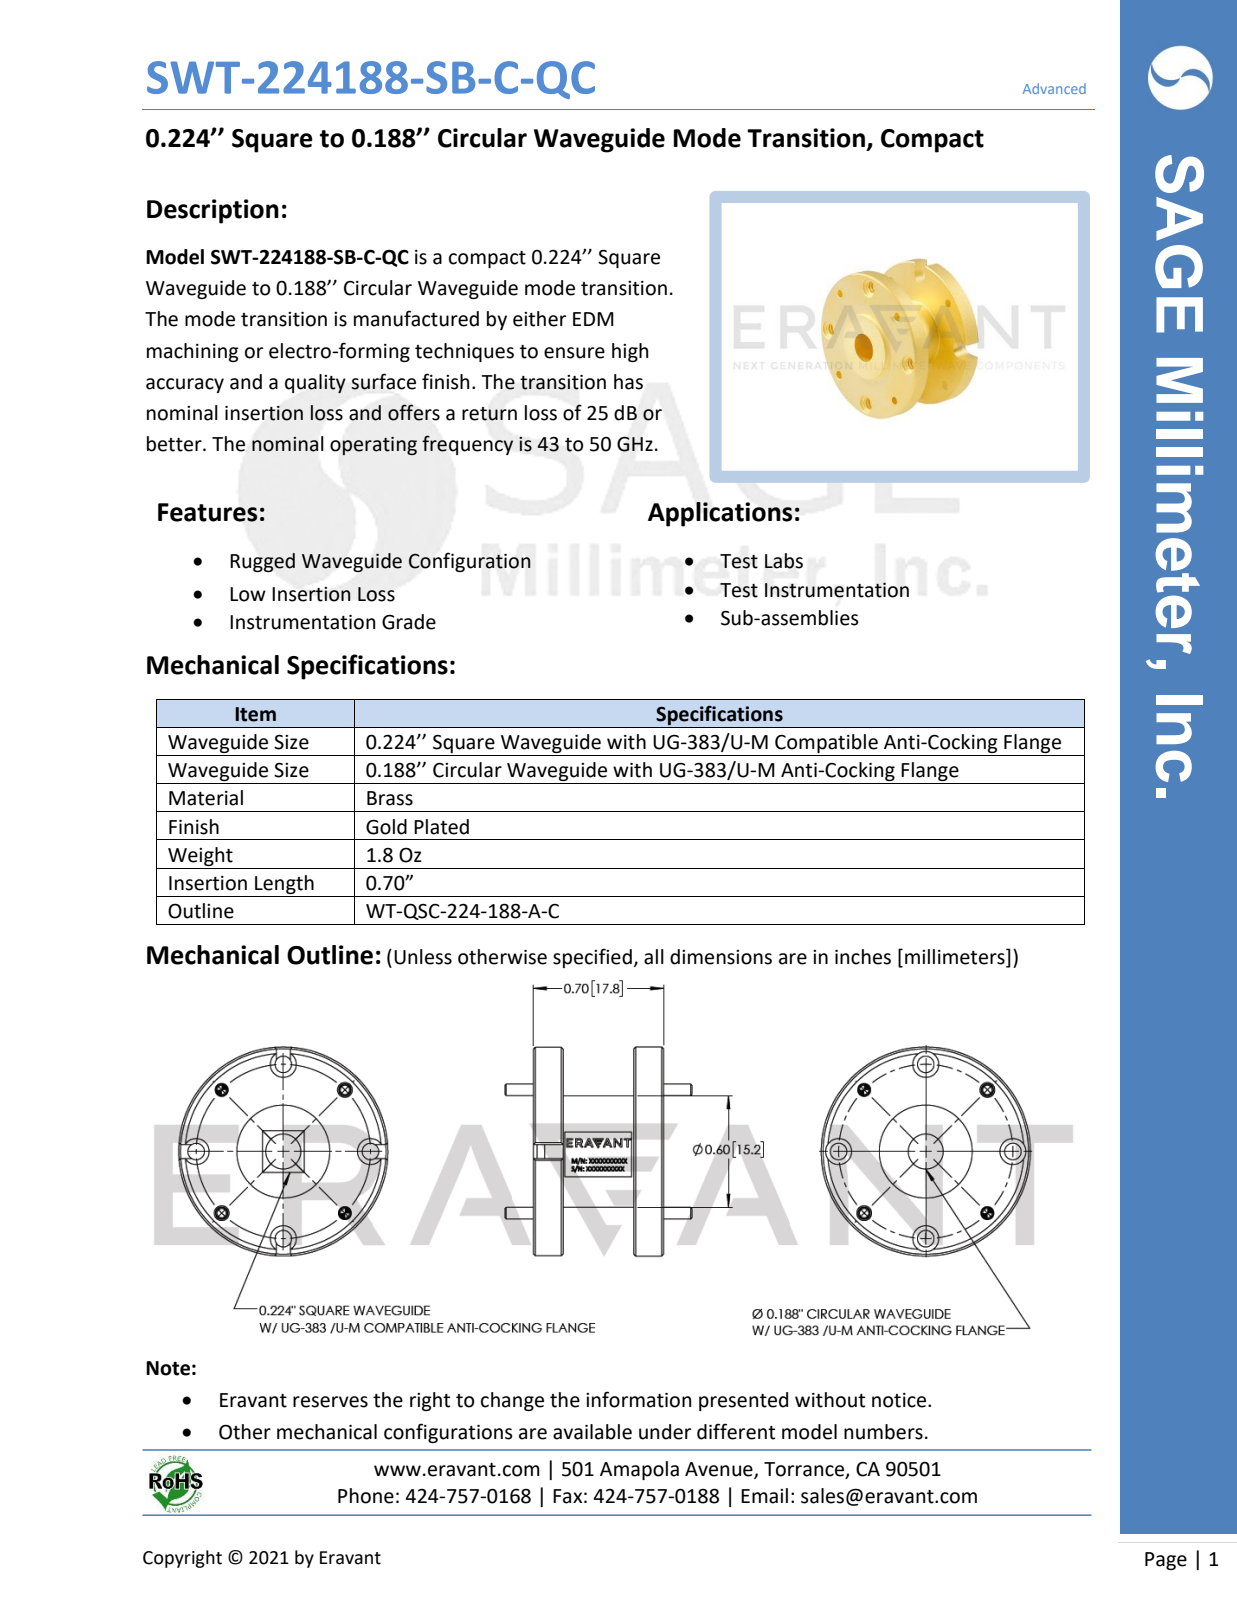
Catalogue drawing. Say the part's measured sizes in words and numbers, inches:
The part is named "WT-QSC-224-188-A-C, Defeatured". Its 3-D file was written by "SolidWorks 2021 (AUTOMOTIVE_DESIGN)". It is 5 solids with 175 faces: 45 planar, 78 cylindrical and 52 other. Overall it measures 1.125 by 1.125 by 1.005 inches. Its volume is 0.385 cubic inches and its surface area 6.001 square inches. Round holes: 4 of diameter 0.061, 4 of diameter 0.067, 4 of diameter 0.089, 4 of diameter 0.14, 1 of diameter 1.055. Round bosses or shafts: 4 of diameter 0.063, 1 of diameter 1.125, 1 of diameter 1.125, 1 of diameter 0.6, 1 of diameter 0.5. The main face-to-face distances are 0.14, 0.52, 0.38, 0.66, 0.02, 0.16, 0.54, 0.68, 0.7, 0.69. The hole center spacings are 0.359, 0.469, 0.663, 0.866, 0.938.
